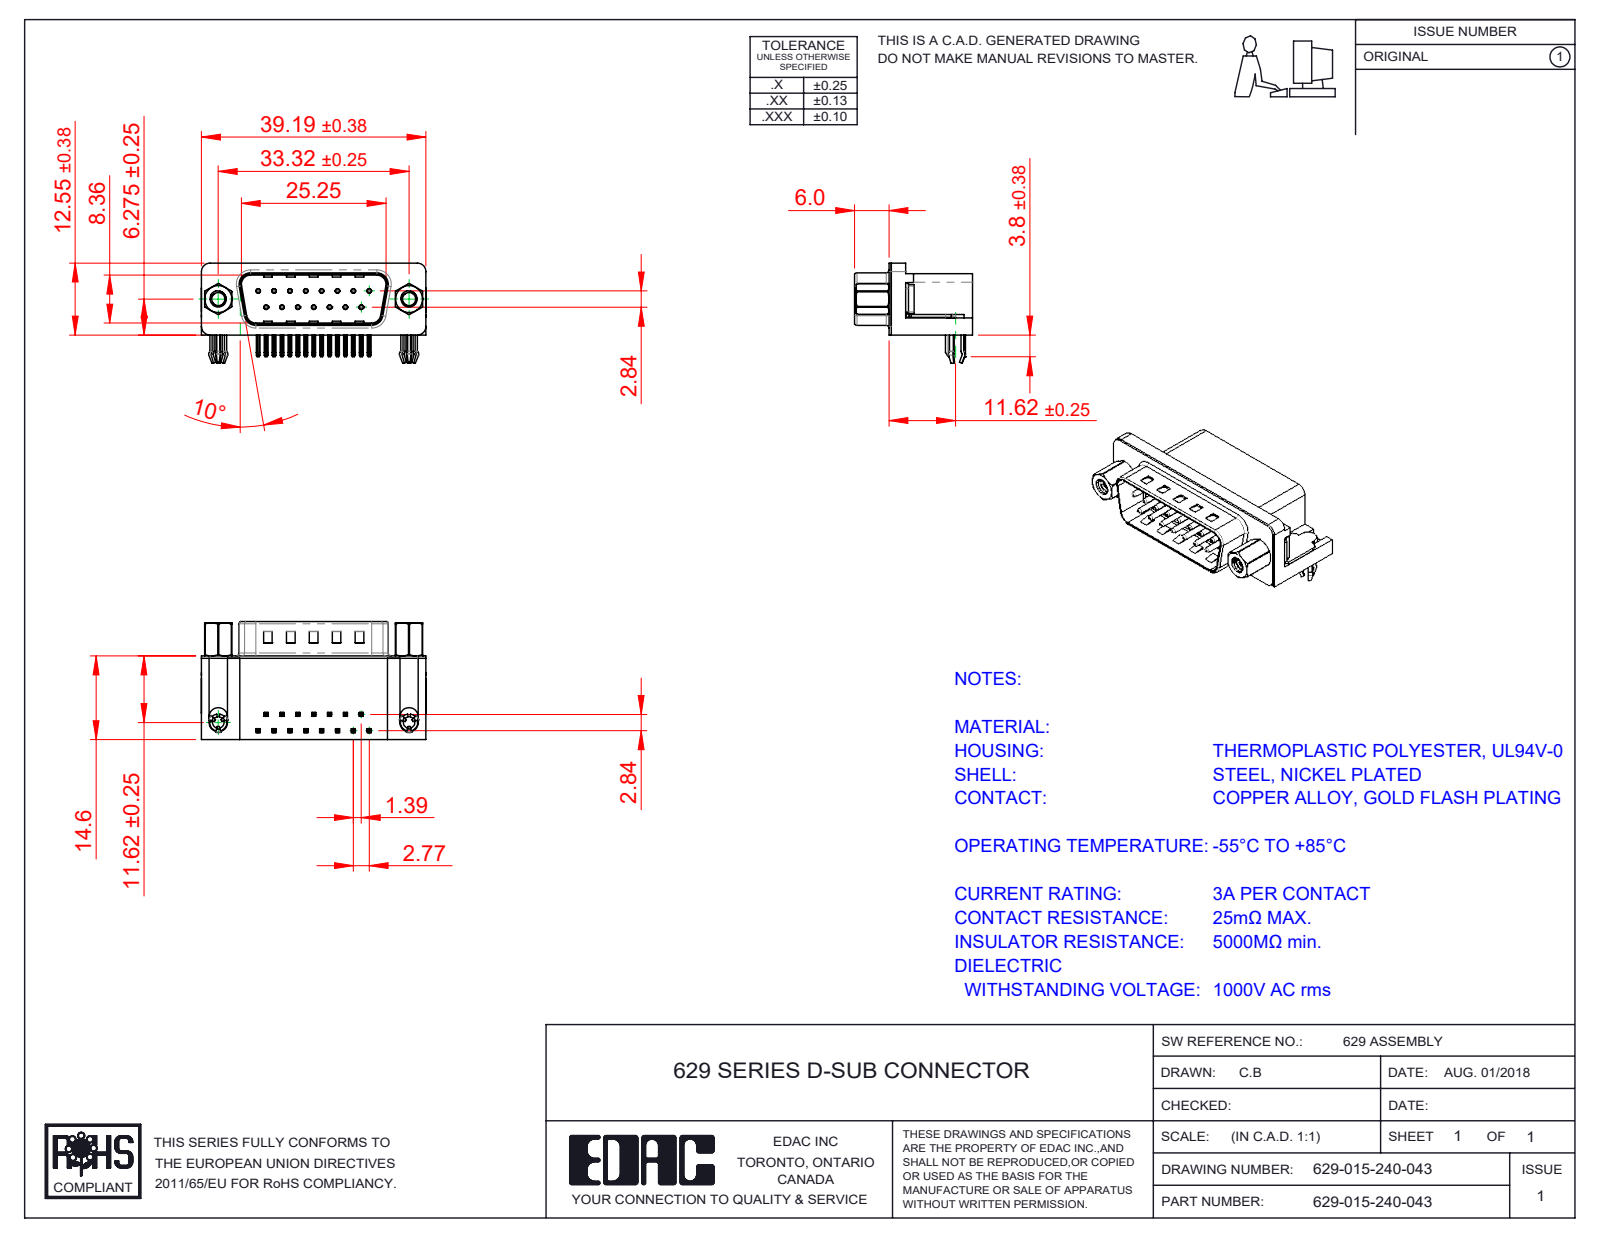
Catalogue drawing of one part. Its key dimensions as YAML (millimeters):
part_name: "629 Contact Top; 629 Shell_15 Socket; 629 3 Prong Board Lock; 629 4-40 Hex Standoff 5 (+4 more)"
step_written_by: "SolidWorks 2020 (CONFIG_CONTROL_DESIGN)"
units: millimeters
bodies: {solids: 23, faces: 1705, planar: 951, cylindrical: 523, other: 231}
overall_size: [39.22, 20.6, 17.48]
volume: 5303
surface_area: 6616
round_holes:
  - {diameter: 0.35, count: 15}
  - {diameter: 0.8, count: 15}
  - {diameter: 2, count: 2}
  - {diameter: 2.26, count: 2}
  - {diameter: 2.29, count: 2}
  - {diameter: 4, count: 2}
  - {diameter: 4.8, count: 2}
  - {diameter: 5, count: 2}
round_bosses_or_shafts:
  - {diameter: 0.75, count: 15}
  - {diameter: 4.9, count: 2}
  - {diameter: 4.75, count: 2}
  - {diameter: 3.9, count: 2}
  - {diameter: 3, count: 2}
  - {diameter: 2.79, count: 2}
partial_cylinders:
  - {radius: 0.25, count: 72}
  - {radius: 0.12, count: 30}
  - {radius: 1, count: 16}
  - {radius: 0.5, count: 9}
  - {radius: 1.6, count: 8}
  - {radius: 1.5, count: 6}
  - {radius: 0.9, count: 4}
  - {radius: 2, count: 4}
face_to_face_distances: [0.4, 14.2, 10.35, 14.6, 2.1, 10.46, 1.7, 10.86, 8.76, 2.9]
hole_center_spacings: [3.16, 2.77, 5.54, 8.31, 11.08, 5.03, 5.04, 7.48]
